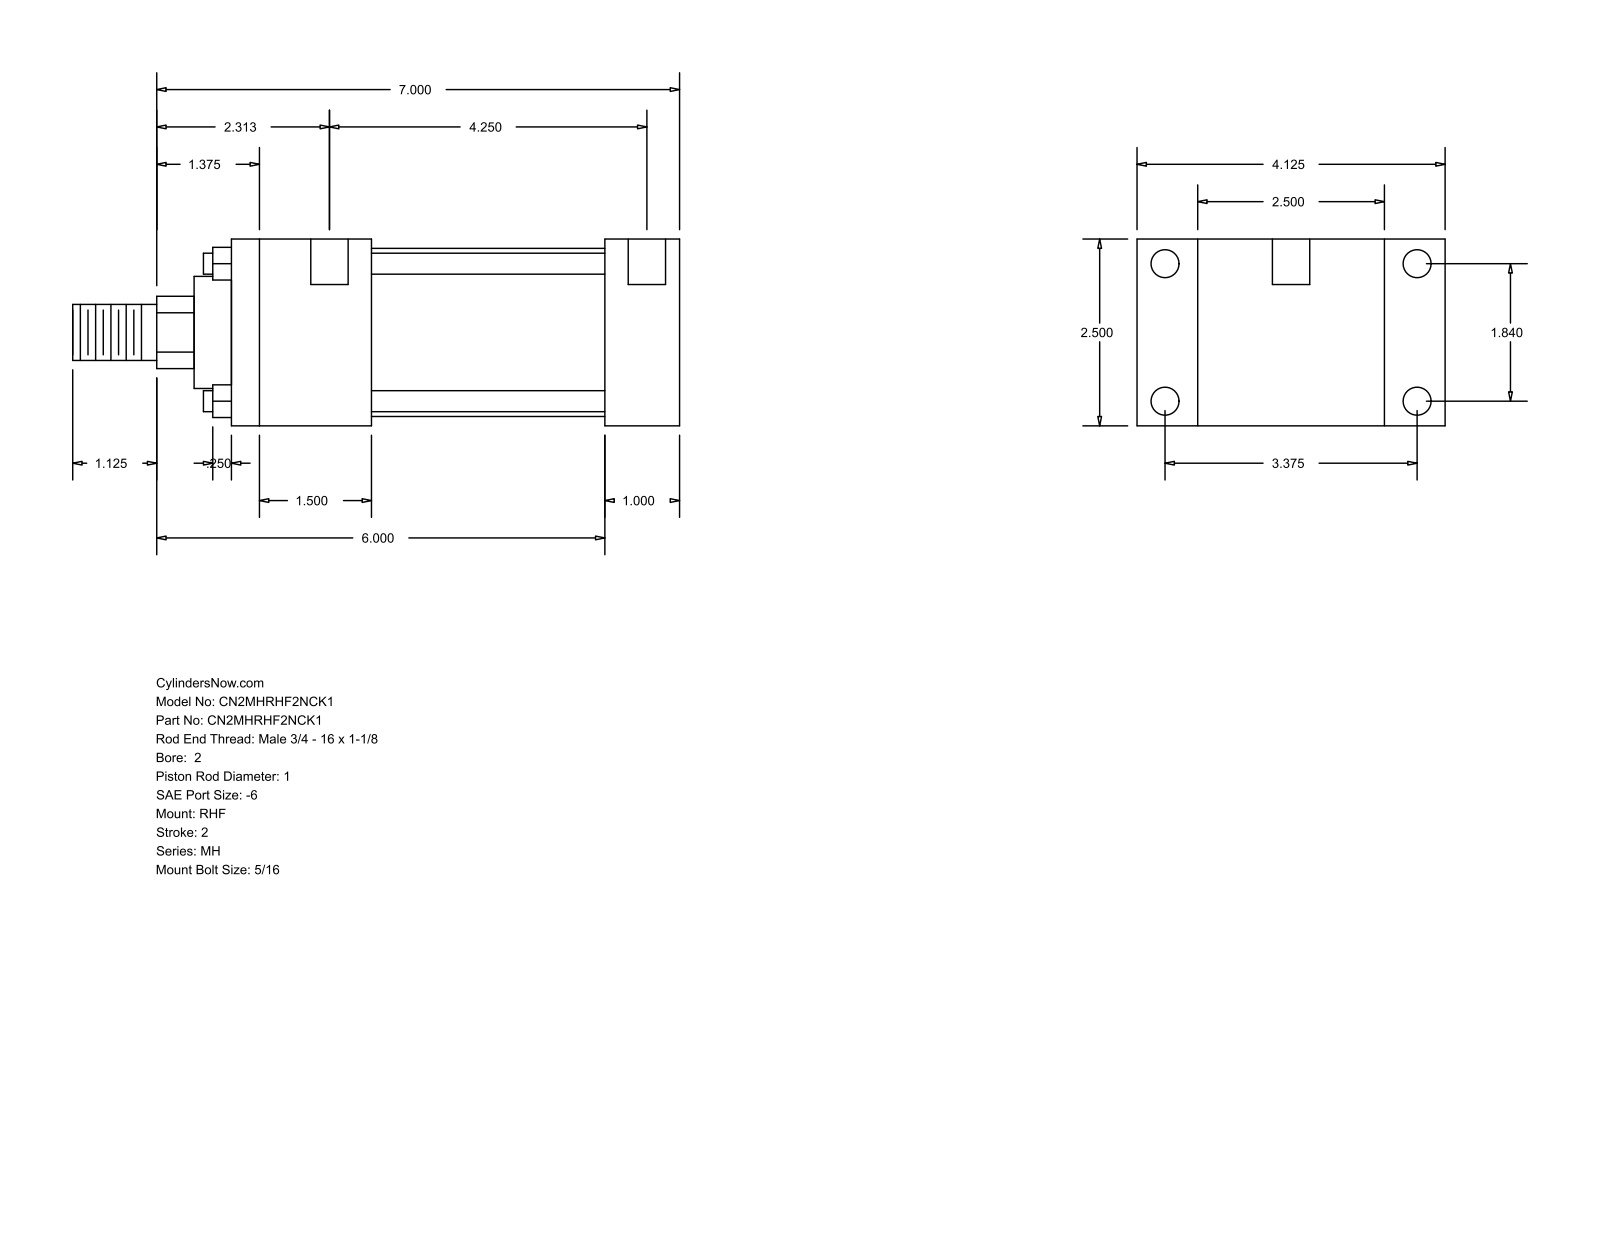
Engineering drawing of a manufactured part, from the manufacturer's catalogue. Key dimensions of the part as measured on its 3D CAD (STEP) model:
Part name (STEP PRODUCT): MH_RHF__0200_1
STEP written by: GSSL Pune (CONFIG_CONTROL_DESIGN)
Units: millimetres
Bodies: 0 solids, 88 faces (60 planar, 28 cylindrical, 0 other)
Overall size (bounding box): 206.38 × 104.78 × 63.5
Round holes (diameter × count): ⌀5.56 ×4, ⌀9.53 ×4, ⌀12.7 ×2
Round bosses / shafts (diameter × count): ⌀7.14 ×4, ⌀57.15 ×1, ⌀38.1 ×1, ⌀25.4 ×1, ⌀19.05 ×1
Partial cylindrical surfaces — rounded edges, fillets, slot ends (radius × count): R12.29 ×1
Main face-to-face distances: 63.5, 25.4, 20.64, 84.14, 152.4, 127, 104.78, 104.77, 47.63, 79.37
Hole centre spacings: 46.74, 85.72, 97.63, 115.88, 3.17, 4.76, 107.95, 111.12
